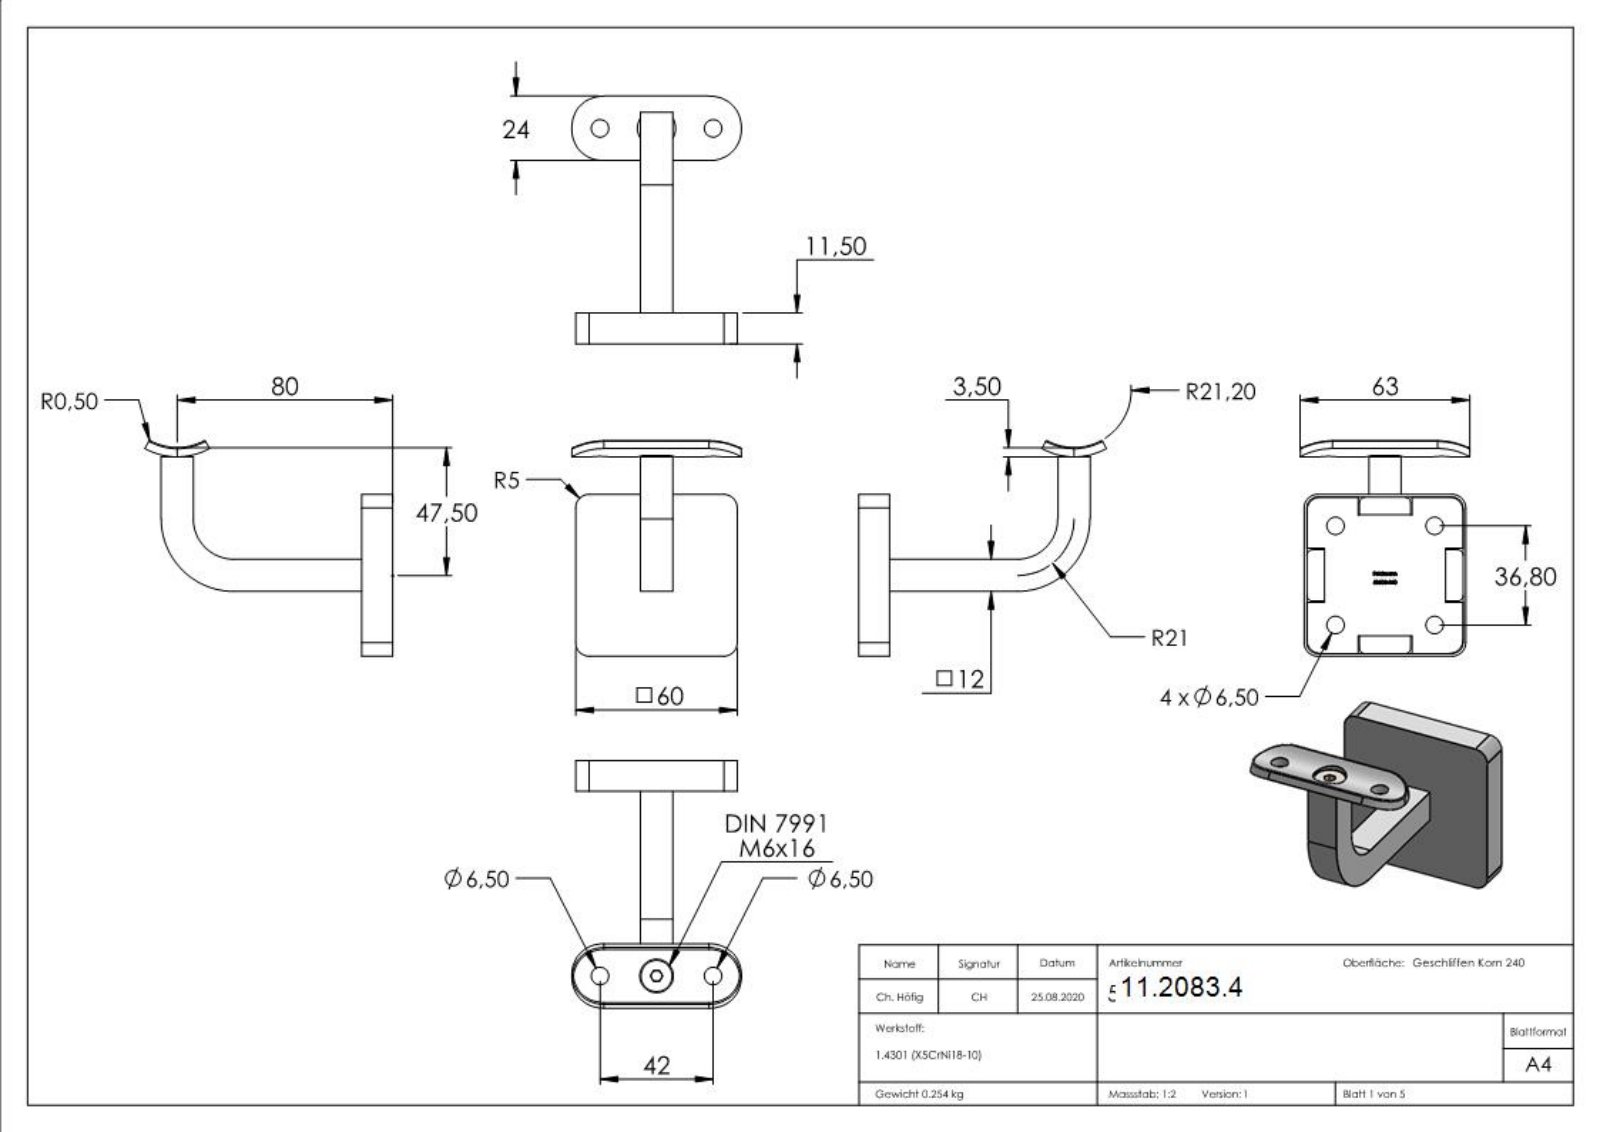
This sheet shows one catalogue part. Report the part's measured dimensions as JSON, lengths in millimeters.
{"part_name": "socket countersunk head screw_din_DIN 7991 - M6 x 16 --- 9.7S; 60182-240_50503-240 Teil3; socket countersunk head screw_din; 50503-240 Teil1 (+5 more)", "step_written_by": "SolidWorks 2018 (CONFIG_CONTROL_DESIGN)", "units": "millimeters", "bodies": {"solids": 4, "faces": 412, "planar": 212, "cylindrical": 56, "other": 144}, "overall_size": [92, 80, 63], "volume_mm3": 32640, "surface_area_mm2": 28693, "round_holes": [[6.5, 6], [5, 1], [12.5, 1]], "round_bosses_or_shafts": [[11.57, 1], [6, 1]], "partial_cylinders_radius": [[2, 12], [5, 8], [4, 4], [12, 4], [0.5, 2], [7.1, 1], [15, 1], [21.2, 1]], "face_to_face_distances": [1, 10.5, 11.5, 9.5, 2, 8.5, 35, 23, 12, 24], "hole_center_spacings": [36.8, 21, 52.04, 42]}
